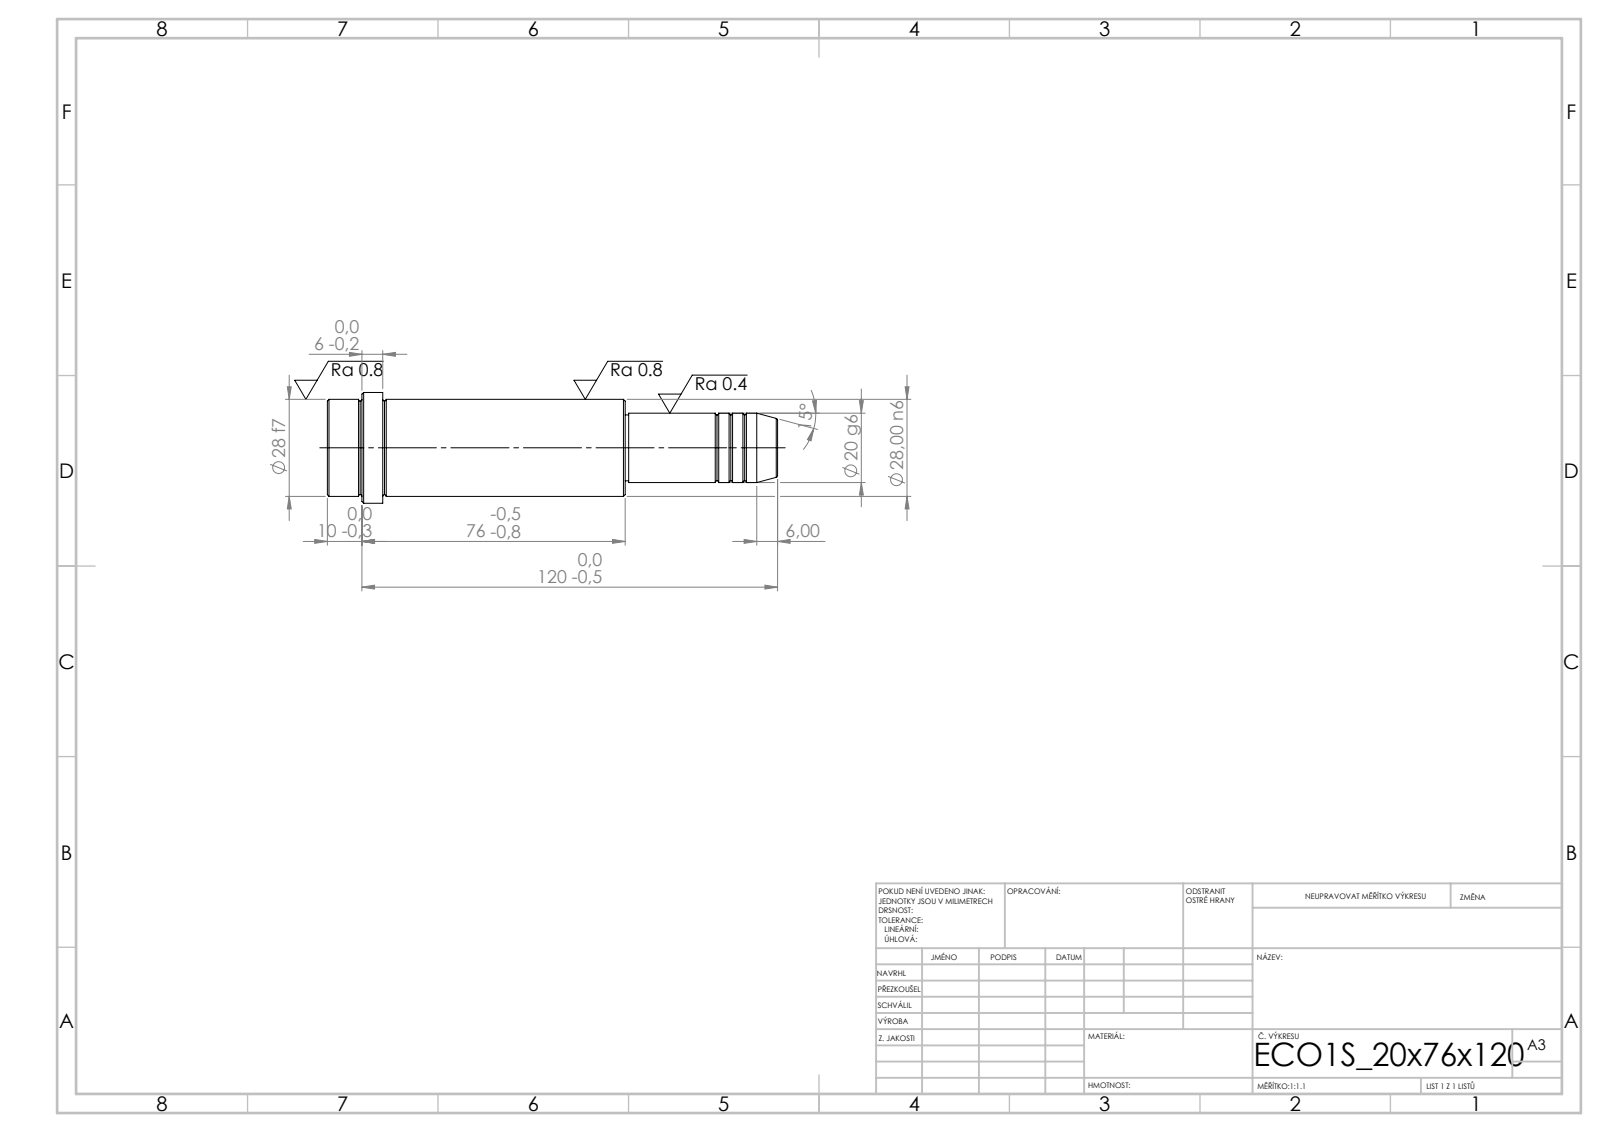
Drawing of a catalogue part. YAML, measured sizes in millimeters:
step_written_by: "SolidWorks 2019 (CONFIG_CONTROL_DESIGN)"
units: millimeters
bodies: {solids: 1, faces: 52, planar: 6, cylindrical: 16, other: 30}
overall_size: [130, 32, 32]
volume: 67415
surface_area: 12065
round_bosses_or_shafts:
  - {diameter: 32, count: 1}
  - {diameter: 28, count: 1}
  - {diameter: 20, count: 1}
  - {diameter: 19, count: 1}
face_to_face_distances: [86, 44, 130, 114, 70, 16, 120, 76, 6, 10]
